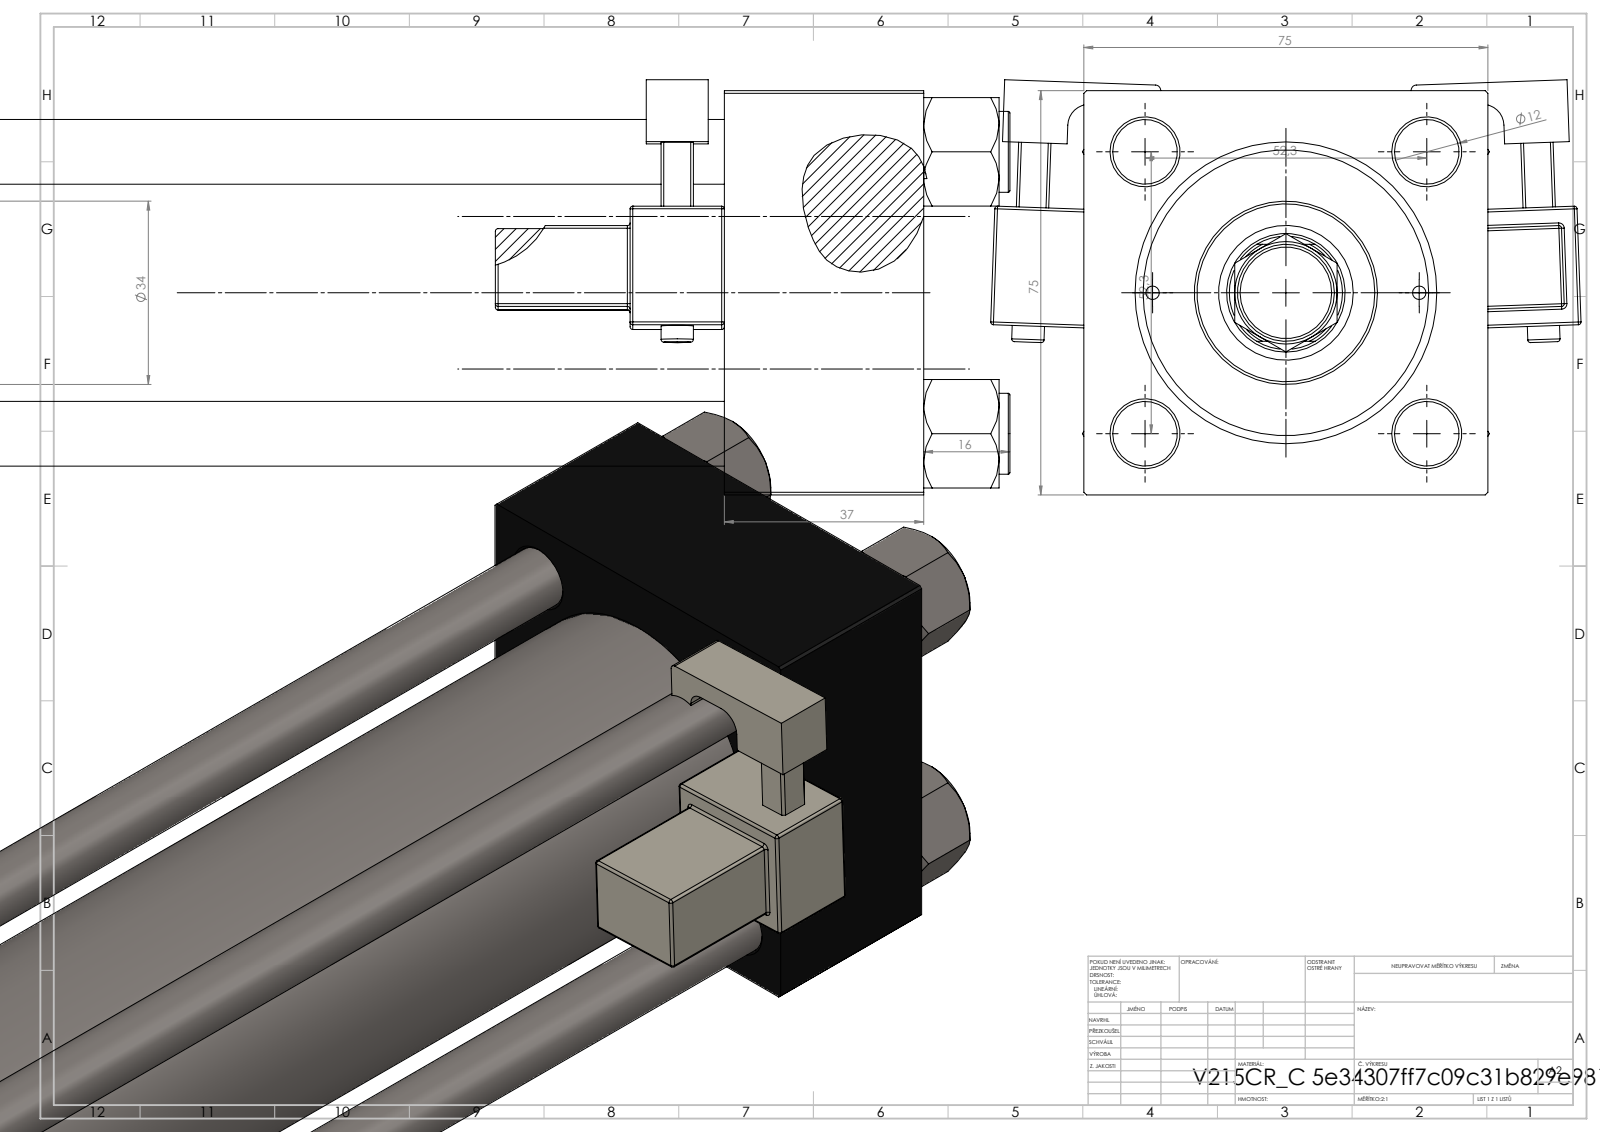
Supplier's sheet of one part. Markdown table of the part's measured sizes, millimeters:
| quantity | value |
| --- | --- |
| part name | V215CR_VCP_C; V215CR_C_TYCINKA; NUT_M5_C; V215CR_MSU (+3 more) |
| STEP written by | SolidWorks 2019 (CONFIG_CONTROL_DESIGN) |
| units | millimeters |
| bodies | 14 solids, 1360 faces (602 planar, 154 cylindrical, 604 other) |
| overall size | 808 × 109.57 × 77.03 |
| volume | 1 479 000 mm³ |
| surface area | 483 024 mm² |
| round holes (diameter × count) | 12 × 4, 2.5 × 2, 7 × 2, 20.96 × 2, 30 × 2, 10.5 × 1, 22 × 1, 25 × 1, 41 × 1, 50 × 1, 53 × 1 |
| round bosses / shafts (diameter × count) | 15 × 4, 6 × 2, 56 × 1, 34 × 1, 18 × 1, 11 × 1 |
| partial cylindrical surfaces (radius × count) | 0.5 × 48, 1 × 2, 2.5 × 2, 4 × 2, 10.5 × 1 |
| main face-to-face distances | 75, 37, 734, 697, 675, 638, 59, 705.3, 668.3, 30.3 |
| hole center spacings | 26.19, 36.98, 52.3, 57.22, 24.75, 73.96, 49.5, 673.5 |
